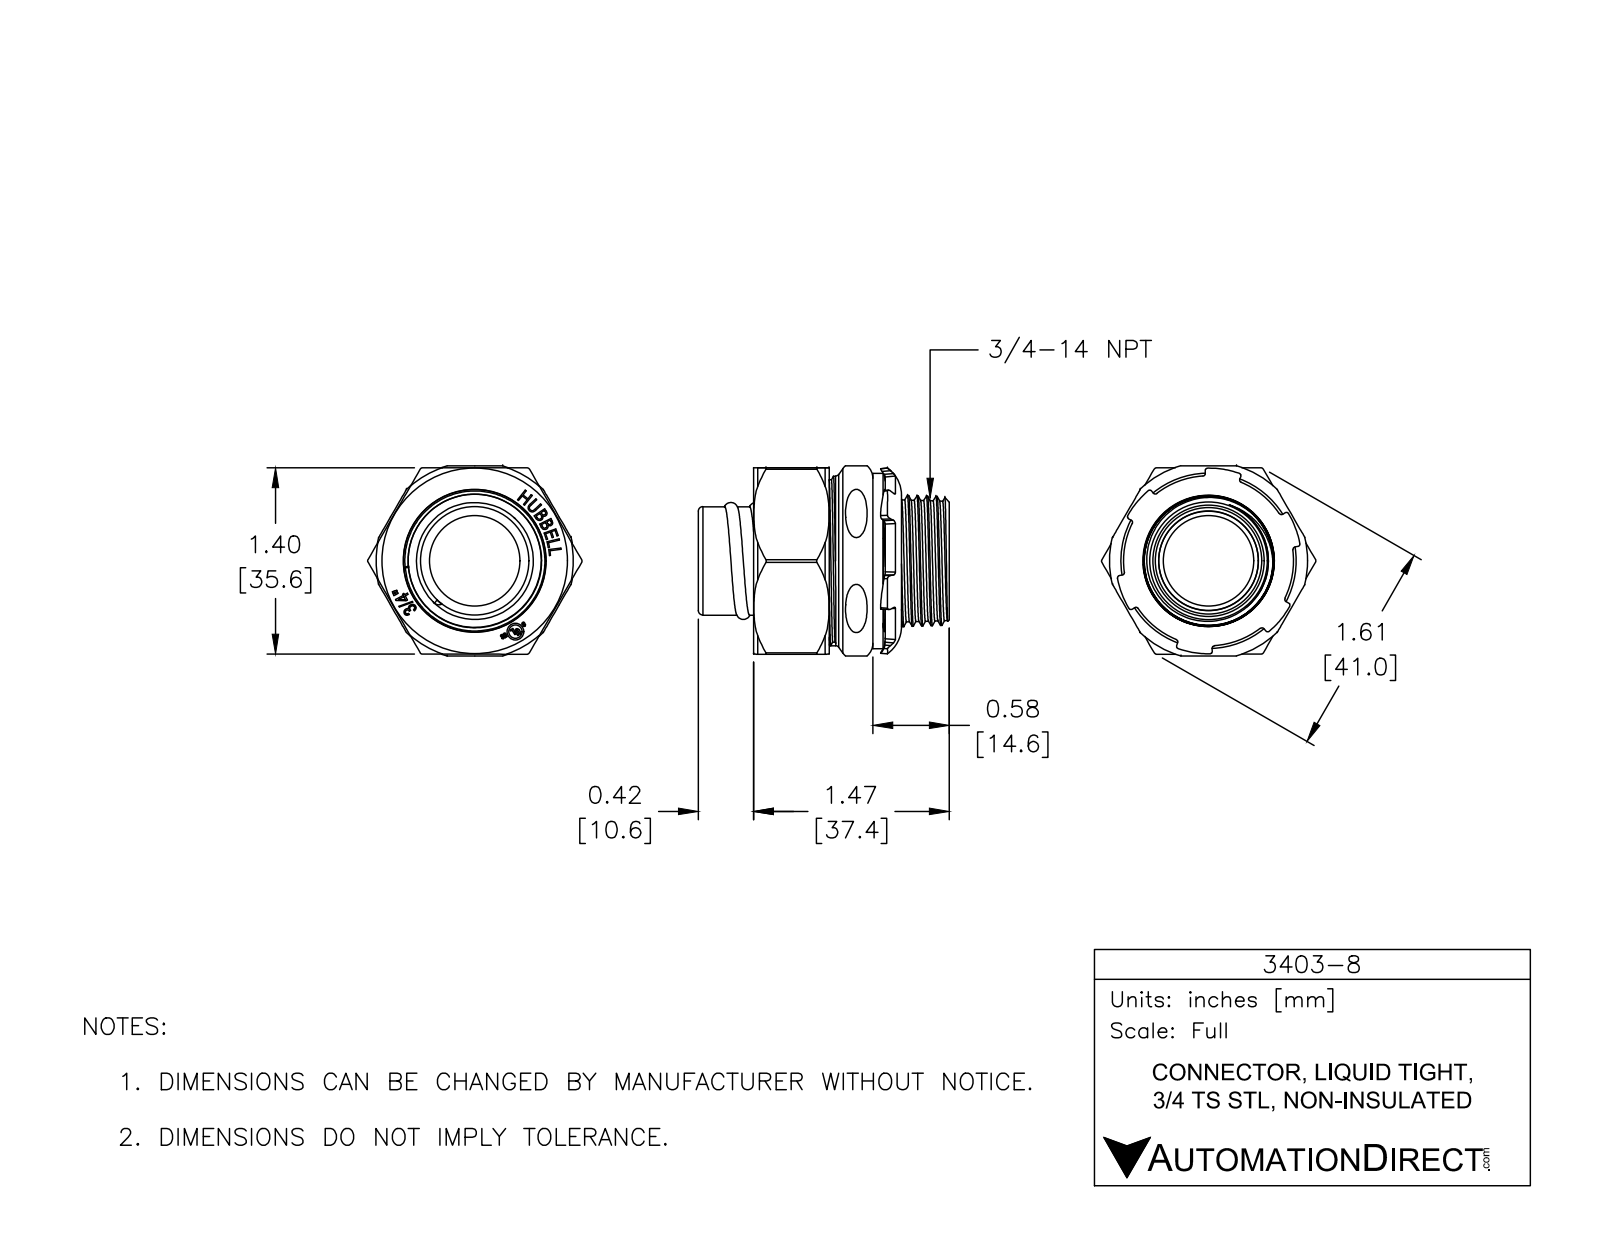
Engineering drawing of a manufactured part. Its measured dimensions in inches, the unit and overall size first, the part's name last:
Units: inches
Overall size (bounding box): 1.888 × 1.613 × 1.49
Round holes (diameter × count): ⌀0.125 ×1, ⌀0.682 ×1, ⌀0.75 ×1, ⌀0.907 ×1, ⌀1.037 ×1, ⌀1.065 ×1, ⌀1.075 ×1, ⌀1.115 ×1, ⌀1.256 ×1, ⌀1.312 ×1
Round bosses / shafts (diameter × count): ⌀1.319 ×1, ⌀1.275 ×1, ⌀1.212 ×1, ⌀1.103 ×1, ⌀0.816 ×1, ⌀0.748 ×1, ⌀0.102 ×1
Partial cylindrical surfaces — rounded edges, fillets, slot ends (radius × count): R0.008 ×8, R0.02 ×6, R0.004 ×1, R0.01 ×1, R0.016 ×1, R0.03 ×1, R0.047 ×1
Main face-to-face distances: 1.402, 0.897, 0.974, 0.077, 1.403, 0.157, 0.817, 0.08, 0.569, 0.248
Hole centre spacings: 0.615
Volume: 0.89 in³ · Surface area: 34.58 in²
Bodies: 6 solids, 517 faces (207 planar, 97 cylindrical, 213 other)
Part name (STEP PRODUCT): 3403 SEAL; 3403 COMPRESSION NUT; 3403 STRAIGHT BODY; 3403-8 (+3 more)
STEP written by: SolidWorks 2014 (AUTOMOTIVE_DESIGN)
